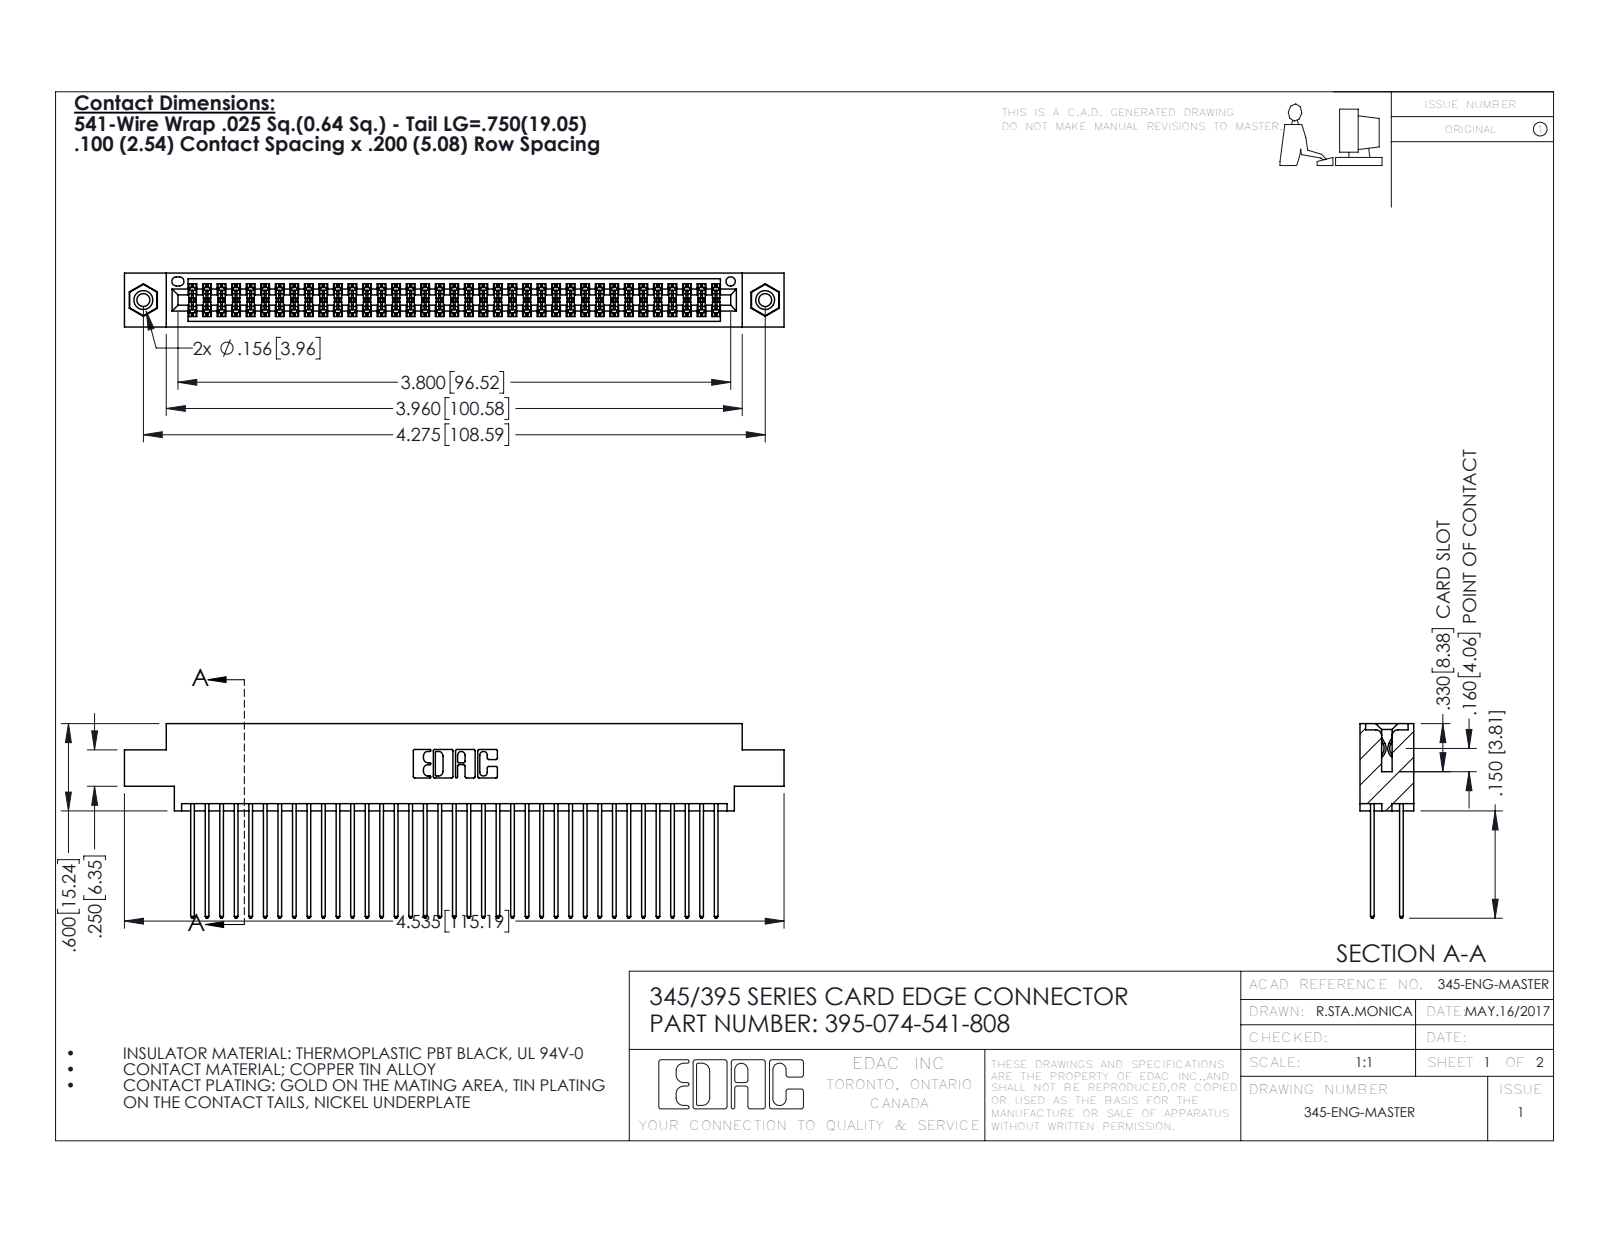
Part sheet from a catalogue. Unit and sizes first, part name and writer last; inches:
Units: inches
Overall size (bounding box): 4.535 × 1.337 × 0.37
Round holes (diameter × count): ⌀0.089 ×2, ⌀0.125 ×2, ⌀0.156 ×2, ⌀0.064 ×1
Round bosses / shafts (diameter × count): ⌀0.155 ×2
Partial cylindrical surfaces — rounded edges, fillets, slot ends (radius × count): R0.006 ×111, R0.01 ×74, R0.01 ×22, R0.007 ×6, R0.031 ×6, R0.026 ×3, R0.014 ×2, R0.019 ×2
Main face-to-face distances: 0.072, 0.298, 0.2, 0.098, 0.272, 0.025, 0.37, 0.225, 0.175, 0.149
Hole centre spacings: 0.27, 4.039, 4.275
Volume: 0.699 in³ · Surface area: 29.42 in²
Bodies: 77 solids, 3890 faces (2558 planar, 1316 cylindrical, 16 other)
Part name (STEP PRODUCT): 395-074-541-808; 345-292-001_345-293-141; 345 Part_0.170 Offset - 0.156 Dia-TI; 345-250-001_345-250-003-102
STEP written by: SolidWorks 2016 (CONFIG_CONTROL_DESIGN)
